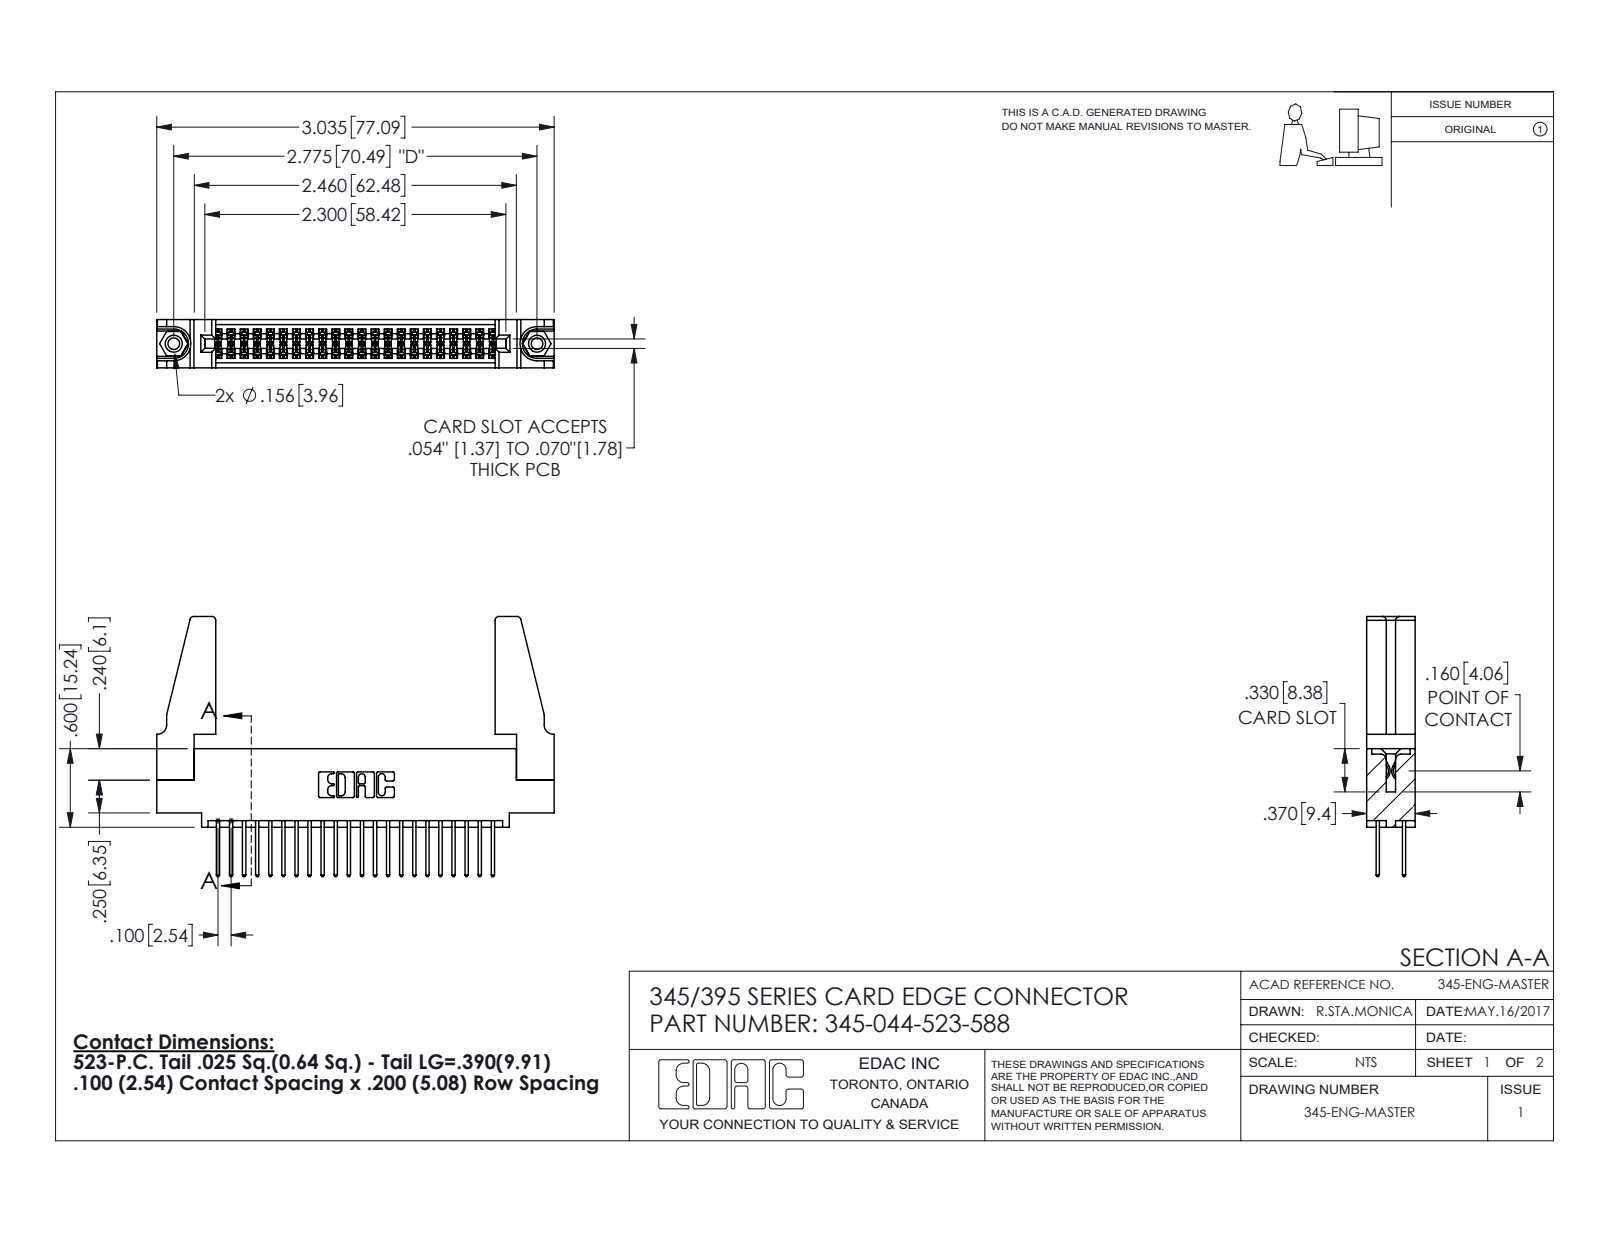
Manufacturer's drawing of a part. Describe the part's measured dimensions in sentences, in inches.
The part is named "345-220-078_345-220-088; 345-250-001_345-250-001-102; 345 Part_0.110 Offset - 0.156 Dia-TH; 345-292-001_345-293-123 (+1 more)". Its 3-D file was written by "SolidWorks 2016 (CONFIG_CONTROL_DESIGN)". It is 49 solids with 2454 faces: 1608 planar, 830 cylindrical and 16 other. Overall it measures 3.036 by 1.987 by 0.37 inches. Its volume is 0.645 cubic inches and its surface area 21.79 square inches. Round holes: 2 of diameter 0.089, 2 of diameter 0.125, 2 of diameter 0.156, 1 of diameter 0.064. Round bosses or shafts: 2 of diameter 0.155. Partial cylindrical surfaces (rounded edges, fillets, slot ends): 66 of radius 0.006, 44 of radius 0.01, 22 of radius 0.01, 8 of radius 0.03, 6 of radius 0.007, 6 of radius 0.031, 3 of radius 0.026, 2 of radius 0.014. The main face-to-face distances are 0.072, 0.298, 0.37, 0.2, 0.098, 0.272, 0.025, 0.225, 0.175, 0.149. The hole center spacings are 0.27, 2.541, 2.775.
